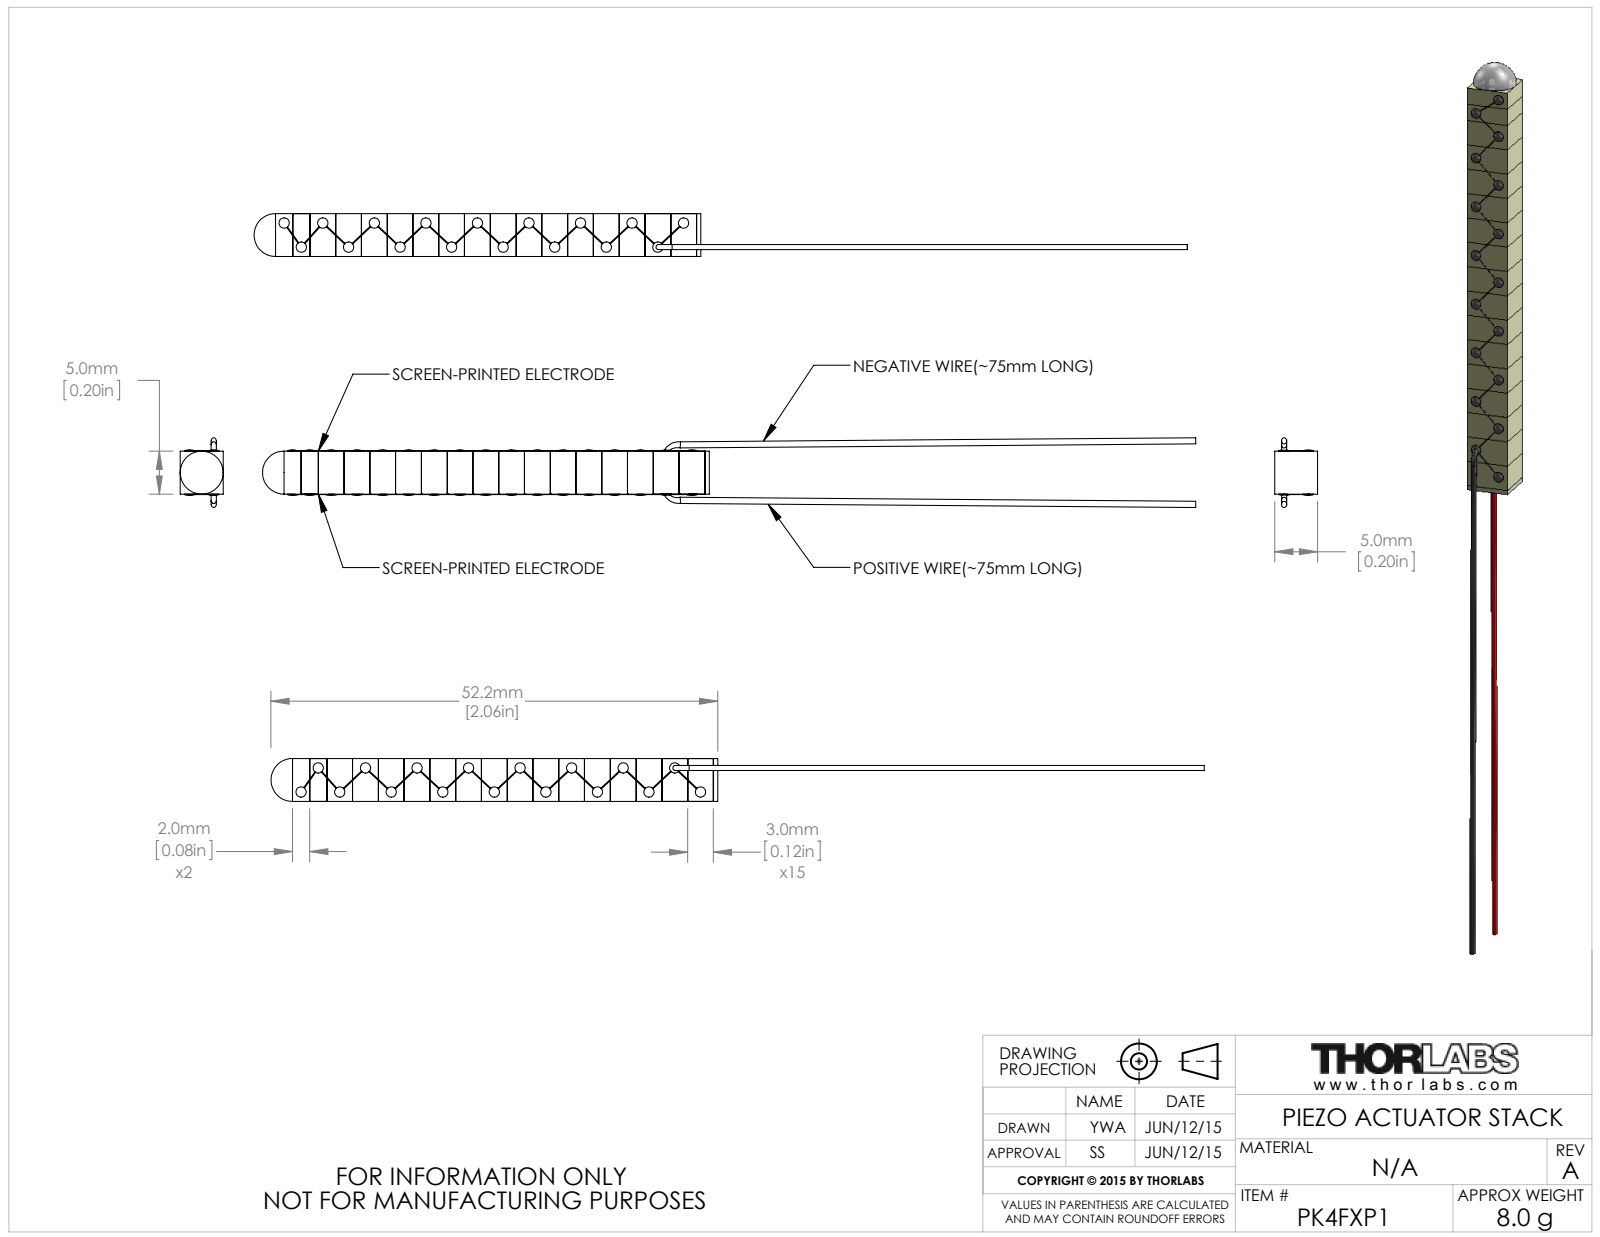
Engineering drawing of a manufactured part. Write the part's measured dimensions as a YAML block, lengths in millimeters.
part_name: "CTN003049"
step_written_by: "SolidWorks 2014 (AUTOMOTIVE_DESIGN)"
units: millimeters
bodies: {solids: 47, faces: 385, planar: 175, cylindrical: 132, other: 78}
overall_size: [108.65, 8.12, 5]
volume: 1517
surface_area: 2595
round_bosses_or_shafts:
  - {diameter: 1.2, count: 17}
face_to_face_distances: [3, 6, 9, 5, 12, 15, 18, 21, 24, 27]
